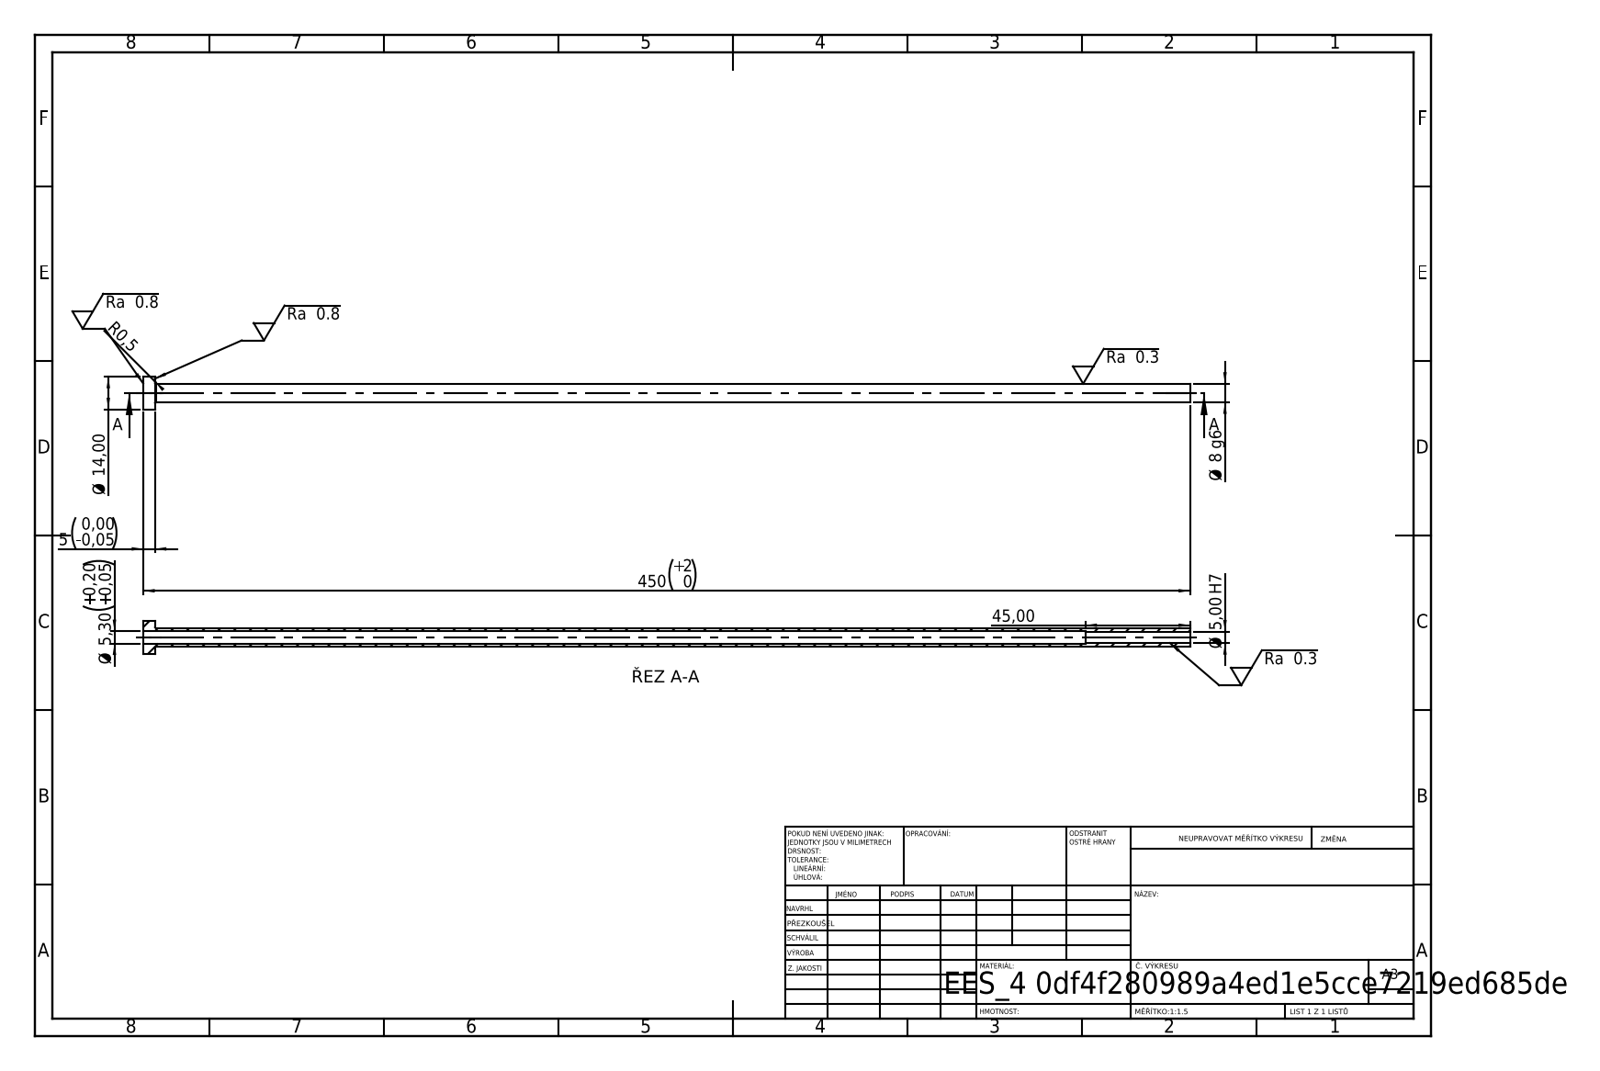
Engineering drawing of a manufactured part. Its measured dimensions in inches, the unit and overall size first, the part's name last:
Units: inches
Overall size (bounding box): 17.717 × 0.551 × 0.551
Round holes (diameter × count): ⌀0.197 ×1, ⌀0.209 ×1
Round bosses / shafts (diameter × count): ⌀0.551 ×1, ⌀0.315 ×1
Main face-to-face distances: 0.197, 17.717, 17.52, 15.945, 15.748, 1.772
Volume: 0.813 in³ · Surface area: 29.63 in²
Bodies: 1 solid, 14 faces (4 planar, 8 cylindrical, 2 other)
STEP written by: SolidWorks 2019 (CONFIG_CONTROL_DESIGN)
